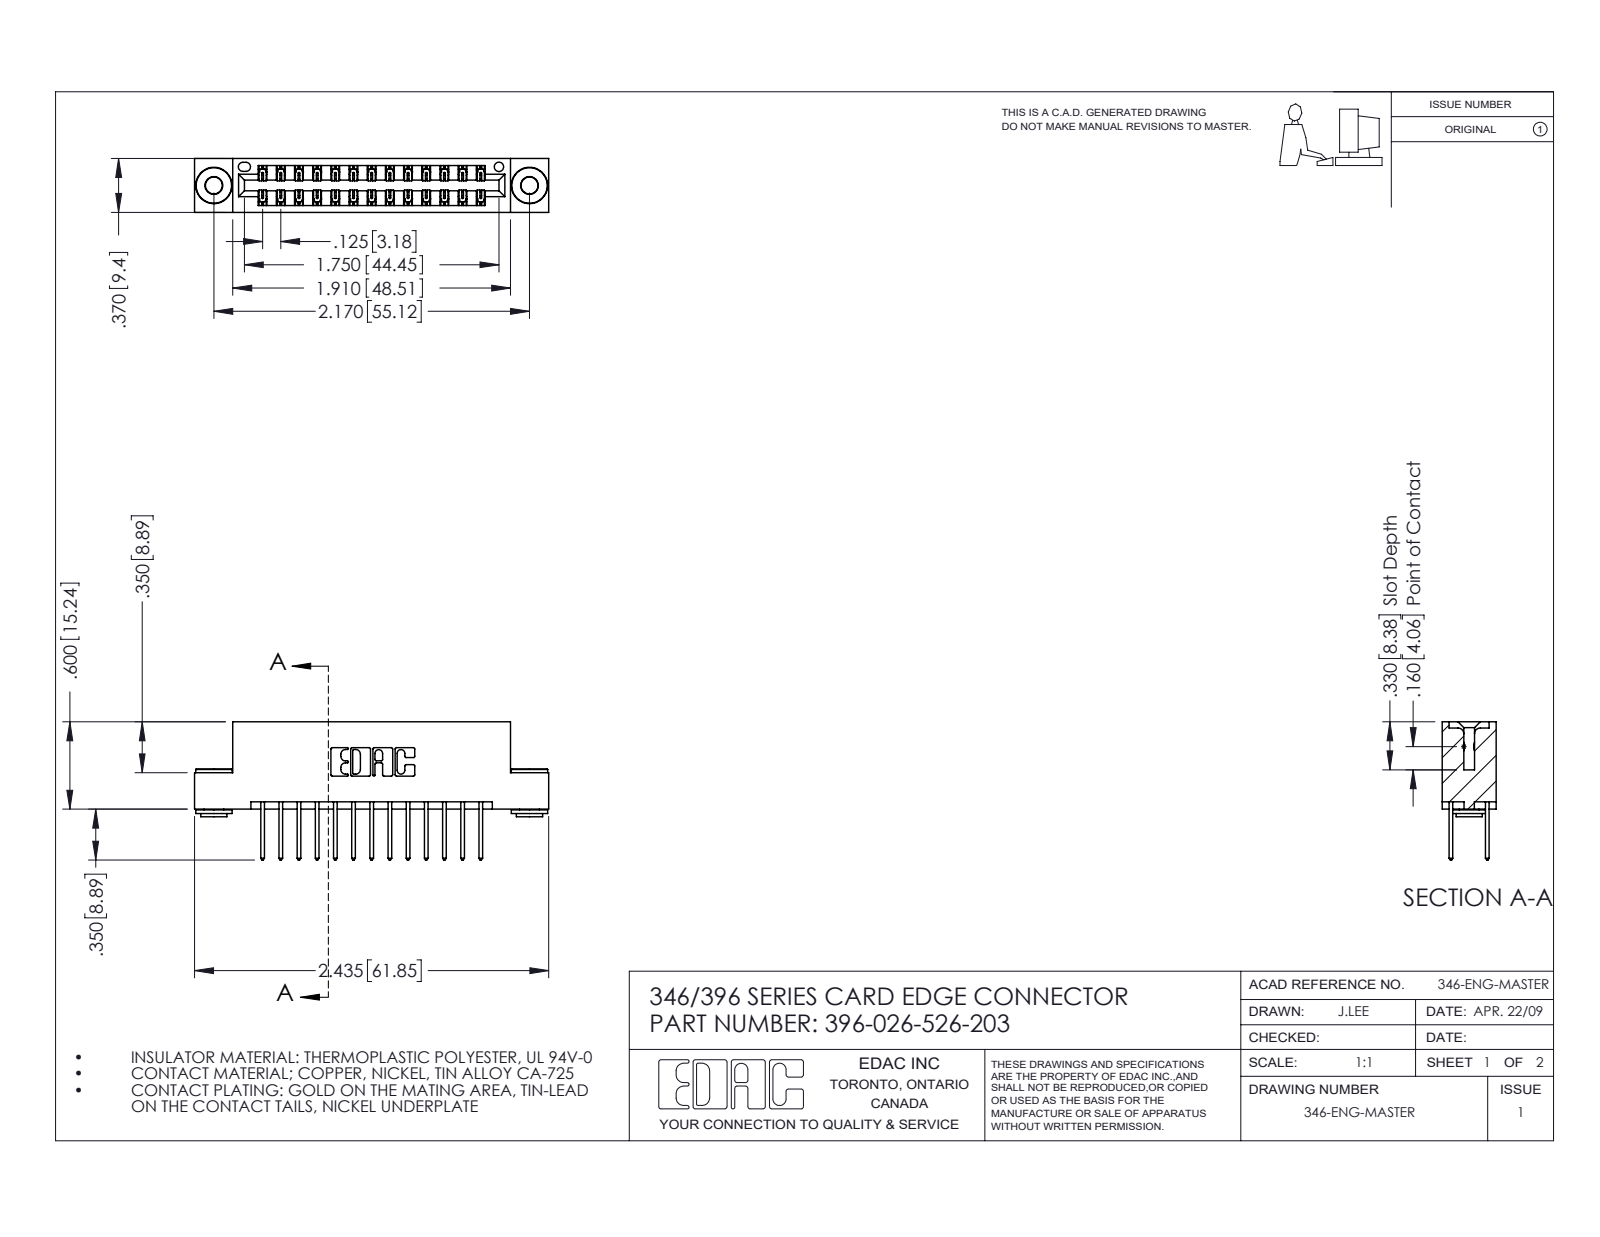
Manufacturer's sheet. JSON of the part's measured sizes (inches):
{"part_name": "396-026-526-203; 345-292-001_345-293-126; 345-250-002_345-250-002-102; 346 Part_Flush Mounting Lugs - 0.156 Dia-TH", "step_written_by": "SolidWorks 2016 (CONFIG_CONTROL_DESIGN)", "units": "inches", "bodies": {"solids": 29, "faces": 1512, "planar": 996, "cylindrical": 508, "other": 8}, "overall_size": [2.435, 0.95, 0.37], "volume_in3": 0.358, "surface_area_in2": 12.42, "round_holes": [[0.116, 2], [0.156, 2], [0.064, 1]], "round_bosses_or_shafts": [[0.25, 2], [0.18, 2], [0.136, 2]], "partial_cylinders_radius": [[0.006, 39], [0.01, 26], [0.01, 22], [0.007, 6], [0.031, 6], [0.026, 3], [0.014, 2], [0.022, 2]], "face_to_face_distances": [0.25, 0.048, 0.322, 0.37, 0.025, 0.072, 0.298, 0.275, 0.148, 0.222], "hole_center_spacings": [0.246, 1.964, 2.17]}
